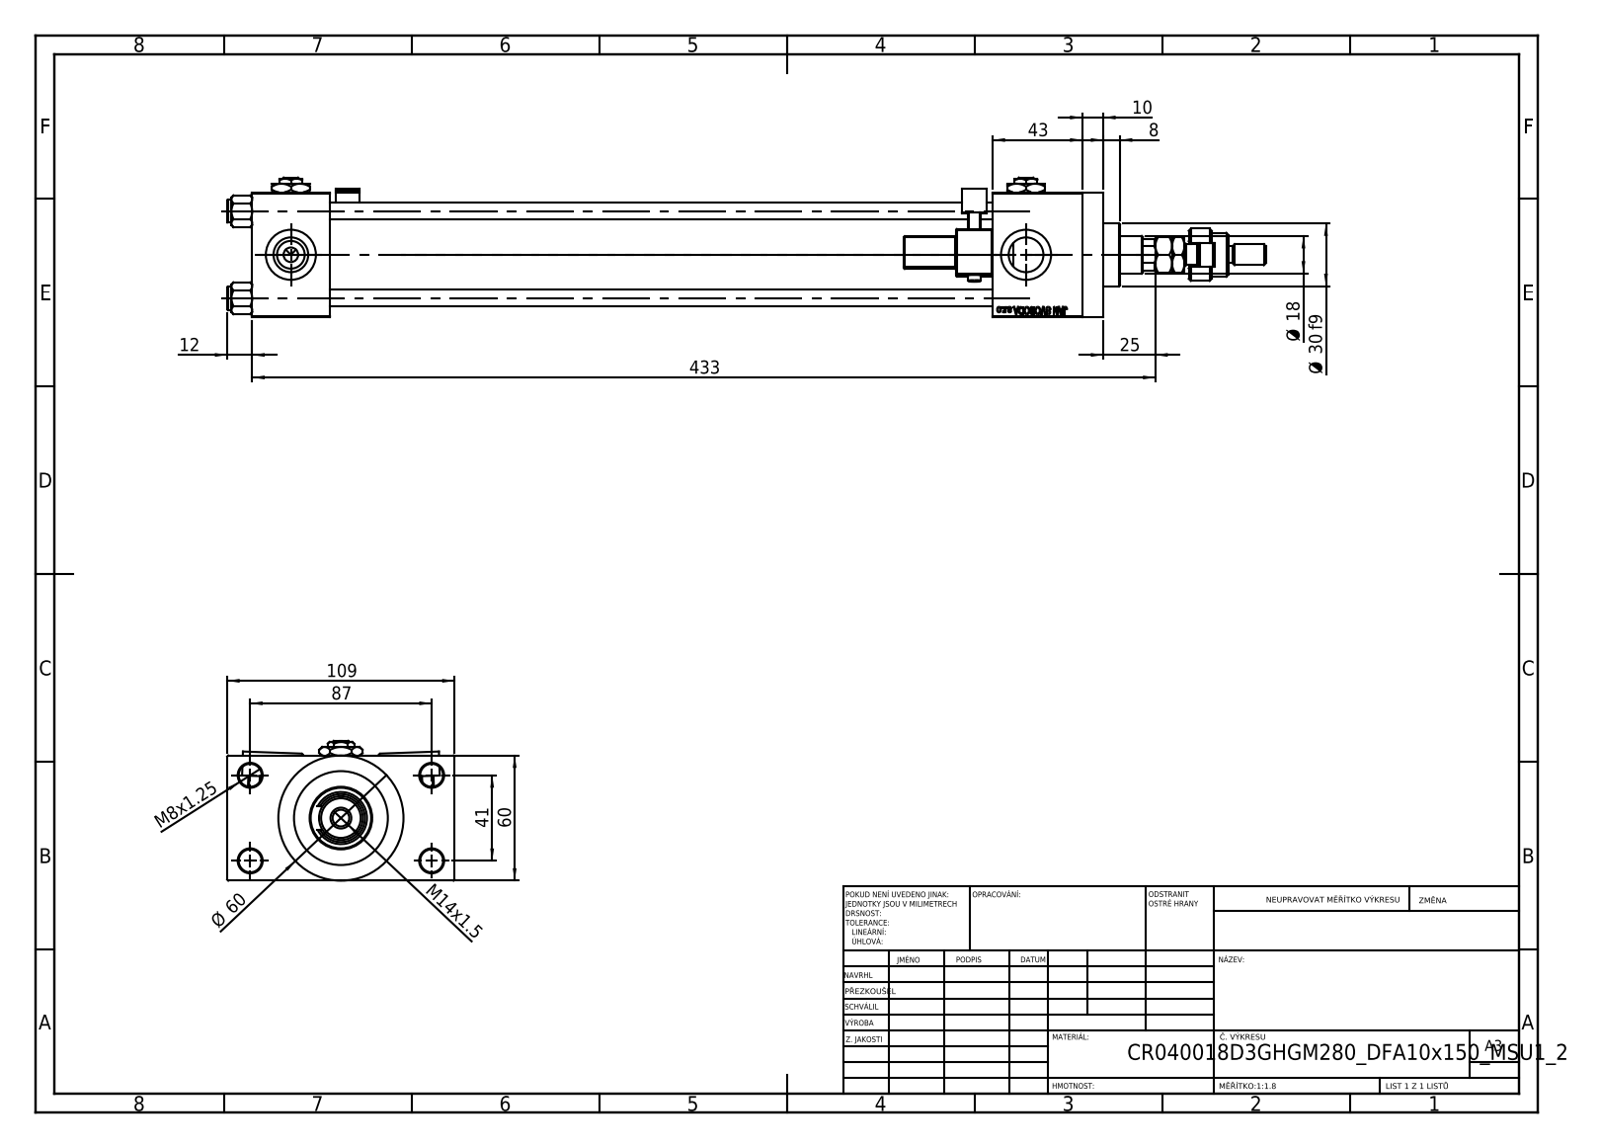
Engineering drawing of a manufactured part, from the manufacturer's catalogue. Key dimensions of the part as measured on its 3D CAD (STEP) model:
Part name (STEP PRODUCT): NUT_M5_D; V215CR_D_Body; V215_VC_A; V215CR_D_TYCINKA (+5 more)
STEP written by: SolidWorks 2019 (CONFIG_CONTROL_DESIGN)
Units: millimetres
Bodies: 17 solids, 1444 faces (632 planar, 172 cylindrical, 640 other)
Overall size (bounding box): 498 × 109 × 67
Volume: 786 775 mm³ · Surface area: 253 811 mm²
Round holes (diameter × count): ⌀8 ×4, ⌀11 ×4, ⌀16.66 ×4, ⌀24 ×4, ⌀7 ×3, ⌀8.5 ×1, ⌀18 ×1, ⌀21 ×1, ⌀31 ×1, ⌀40 ×1, ⌀45 ×1
Round bosses / shafts (diameter × count): ⌀11 ×4, ⌀6 ×2, ⌀60 ×1, ⌀46 ×1, ⌀30 ×1, ⌀25 ×1, ⌀16 ×1, ⌀10 ×1
Partial cylindrical surfaces — rounded edges, fillets, slot ends (radius × count): R0.5 ×48, R1 ×2, R2.5 ×2, R4 ×2, R5.5 ×1, R8.5 ×1, R8.75 ×1
Main face-to-face distances: 60, 318, 24.5, 84.5, 37, 355, 43, 398, 361, 10
Hole centre spacings: 22.65, 29.49, 41.7, 47.15, 48.09, 64.35, 76.49, 41
